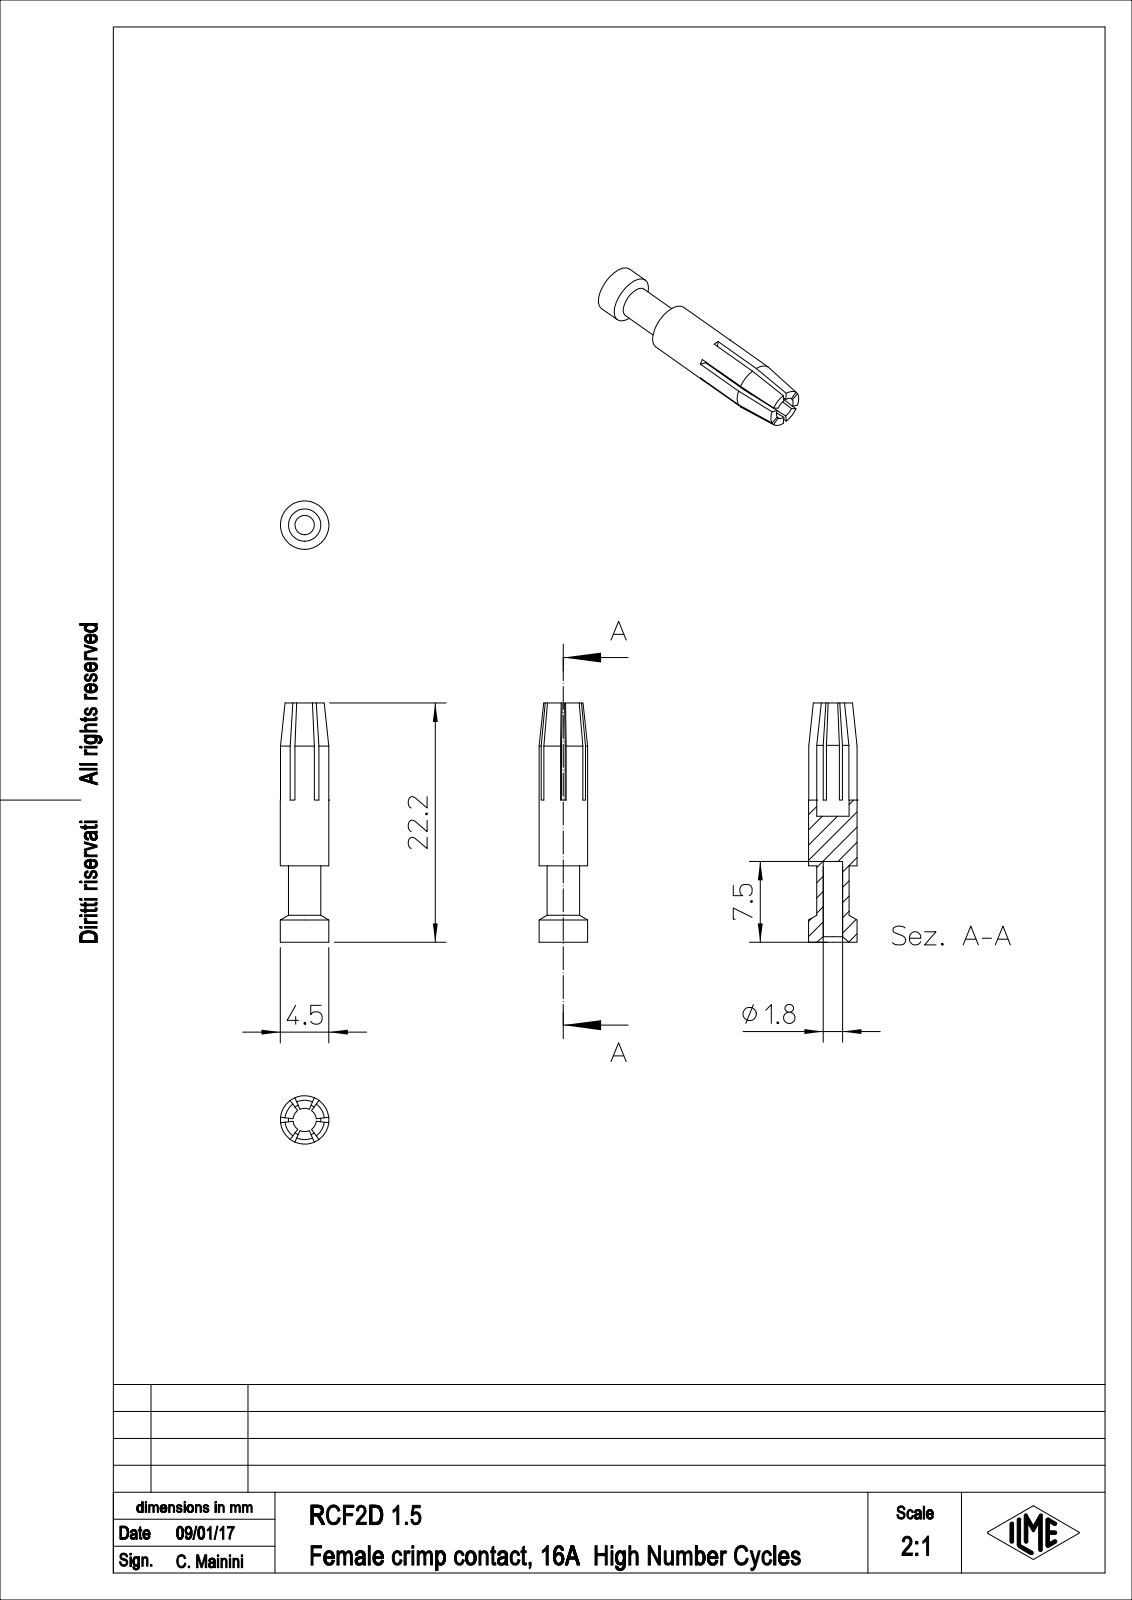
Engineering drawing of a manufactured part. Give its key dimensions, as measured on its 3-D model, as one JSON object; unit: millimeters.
{"part_name": "RCF2D_1.5", "step_written_by": "PTC Creo Elements/Direct Modeling 19.0E 27-Jun-2016 (C) Parametric Technology GmbH (AUTOMOTIVE_DESIGN)", "units": "millimeters", "bodies": {"solids": 1, "faces": 54, "planar": 28, "cylindrical": 10, "other": 16}, "overall_size": [22.2, 4.5, 4.5], "volume_mm3": 196, "surface_area_mm2": 503, "round_holes": [[1.8, 1], [3, 1]], "round_bosses_or_shafts": [[4.5, 1]], "face_to_face_distances": [7.1, 4.6, 11.7, 10.5, 15.1, 22.2, 14.7, 4.2, 0.4, 7.5]}
